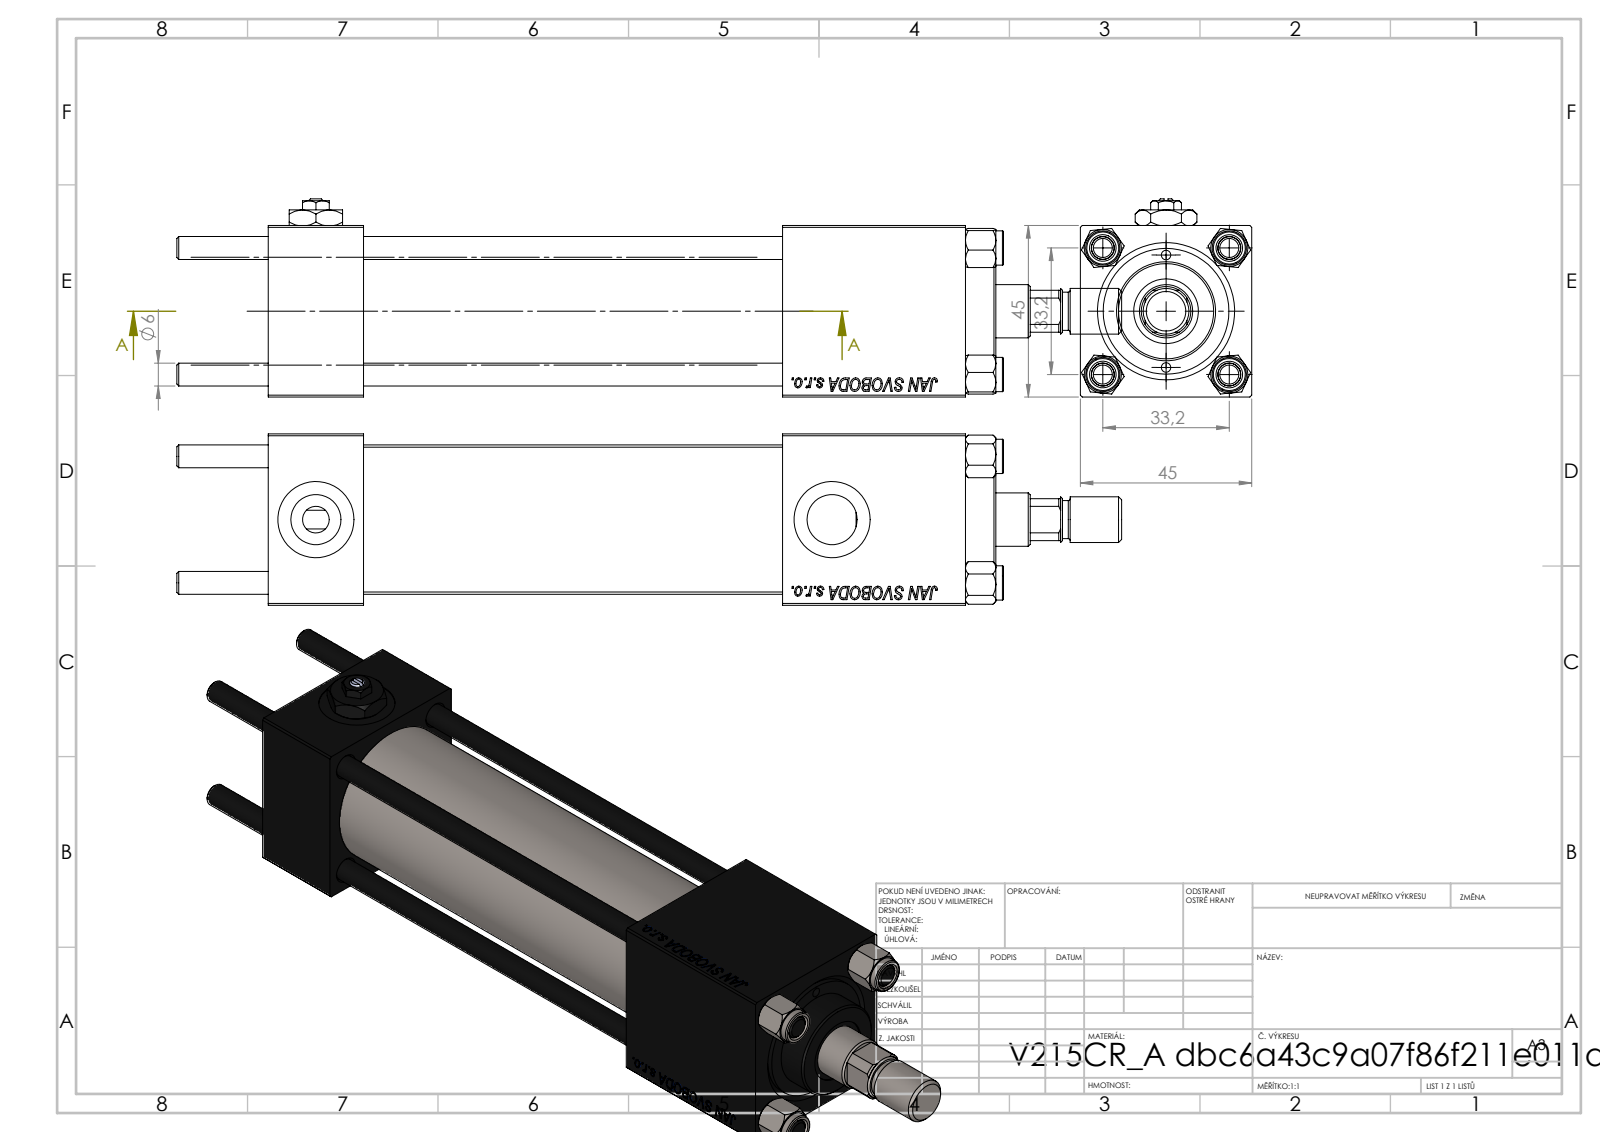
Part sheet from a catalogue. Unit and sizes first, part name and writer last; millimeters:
Units: millimetres
Overall size (bounding box): 248 × 52 × 45
Round holes (diameter × count): ⌀6 ×4, ⌀2.5 ×2, ⌀7 ×2, ⌀13.16 ×2, ⌀20 ×2, ⌀6.5 ×1, ⌀14 ×1, ⌀17 ×1, ⌀24 ×1, ⌀32 ×1, ⌀33 ×1
Round bosses / shafts (diameter × count): ⌀9 ×4, ⌀38 ×1, ⌀26 ×1, ⌀12 ×1, ⌀10 ×1
Partial cylindrical surfaces — rounded edges, fillets, slot ends (radius × count): R6.5 ×1
Main face-to-face distances: 45, 25, 183, 158, 135, 110, 48, 154.3, 129.3, 19.3
Hole centre spacings: 16.7, 23.48, 33.2, 35.47, 14.75, 46.95, 29.5, 135.5
Volume: 234 953 mm³ · Surface area: 95 188 mm²
Bodies: 13 solids, 1204 faces (548 planar, 92 cylindrical, 564 other)
Part name (STEP PRODUCT): NUT_M5; V215CR_BODY_A; V215CR_VCP; ROD_END_AH (+3 more)
STEP written by: SolidWorks 2019 (CONFIG_CONTROL_DESIGN)
